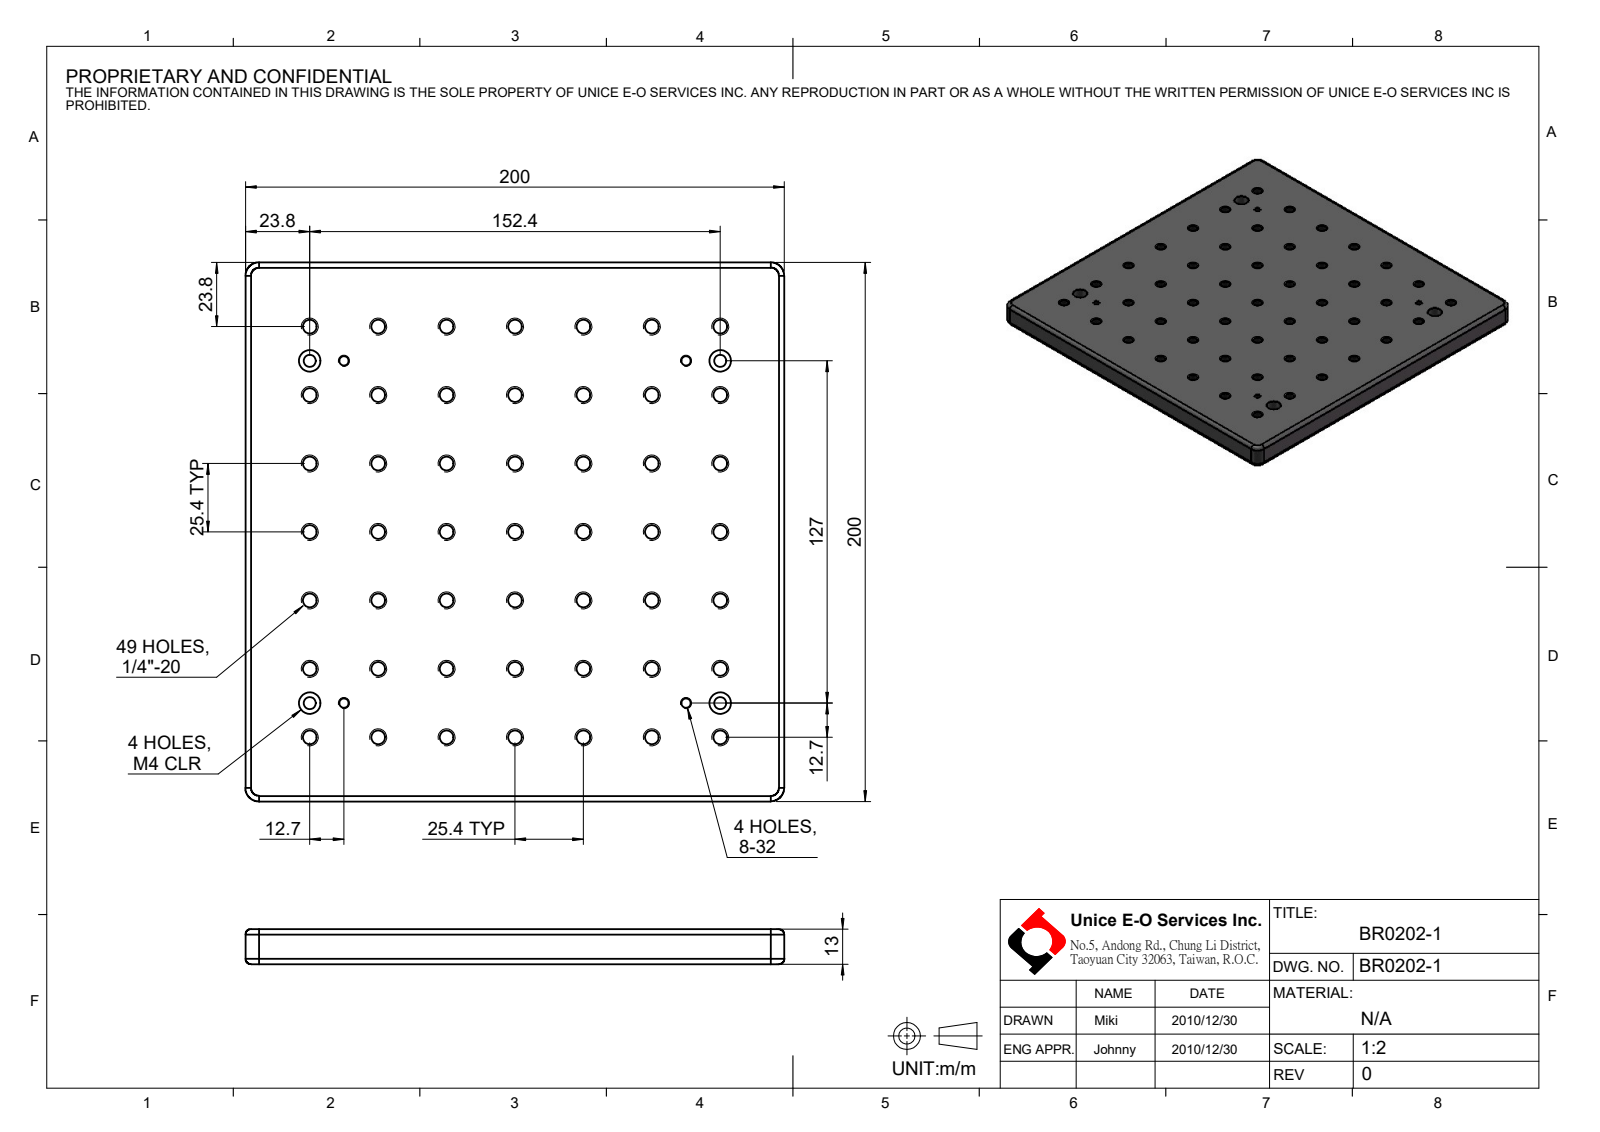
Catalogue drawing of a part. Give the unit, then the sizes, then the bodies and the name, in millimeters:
Units: millimetres
Overall size (bounding box): 200 × 200 × 13
Round holes (diameter × count): ⌀5.11 ×49, ⌀3.45 ×4, ⌀4.5 ×4, ⌀8 ×4
Partial cylindrical surfaces — rounded edges, fillets, slot ends (radius × count): R2 ×8, R5 ×4
Main face-to-face distances: 13, 200, 7, 6
Hole centre spacings: 25.4, 154.5, 127, 50.8, 160.64, 76.2, 140.28, 152.4
Volume: 503 188 mm³ · Surface area: 98 455 mm²
Bodies: 1 solid, 152 faces (10 planar, 134 cylindrical, 8 other)
Part name (STEP PRODUCT): BR0202-1
STEP written by: SolidWorks 2016 (CONFIG_CONTROL_DESIGN)
